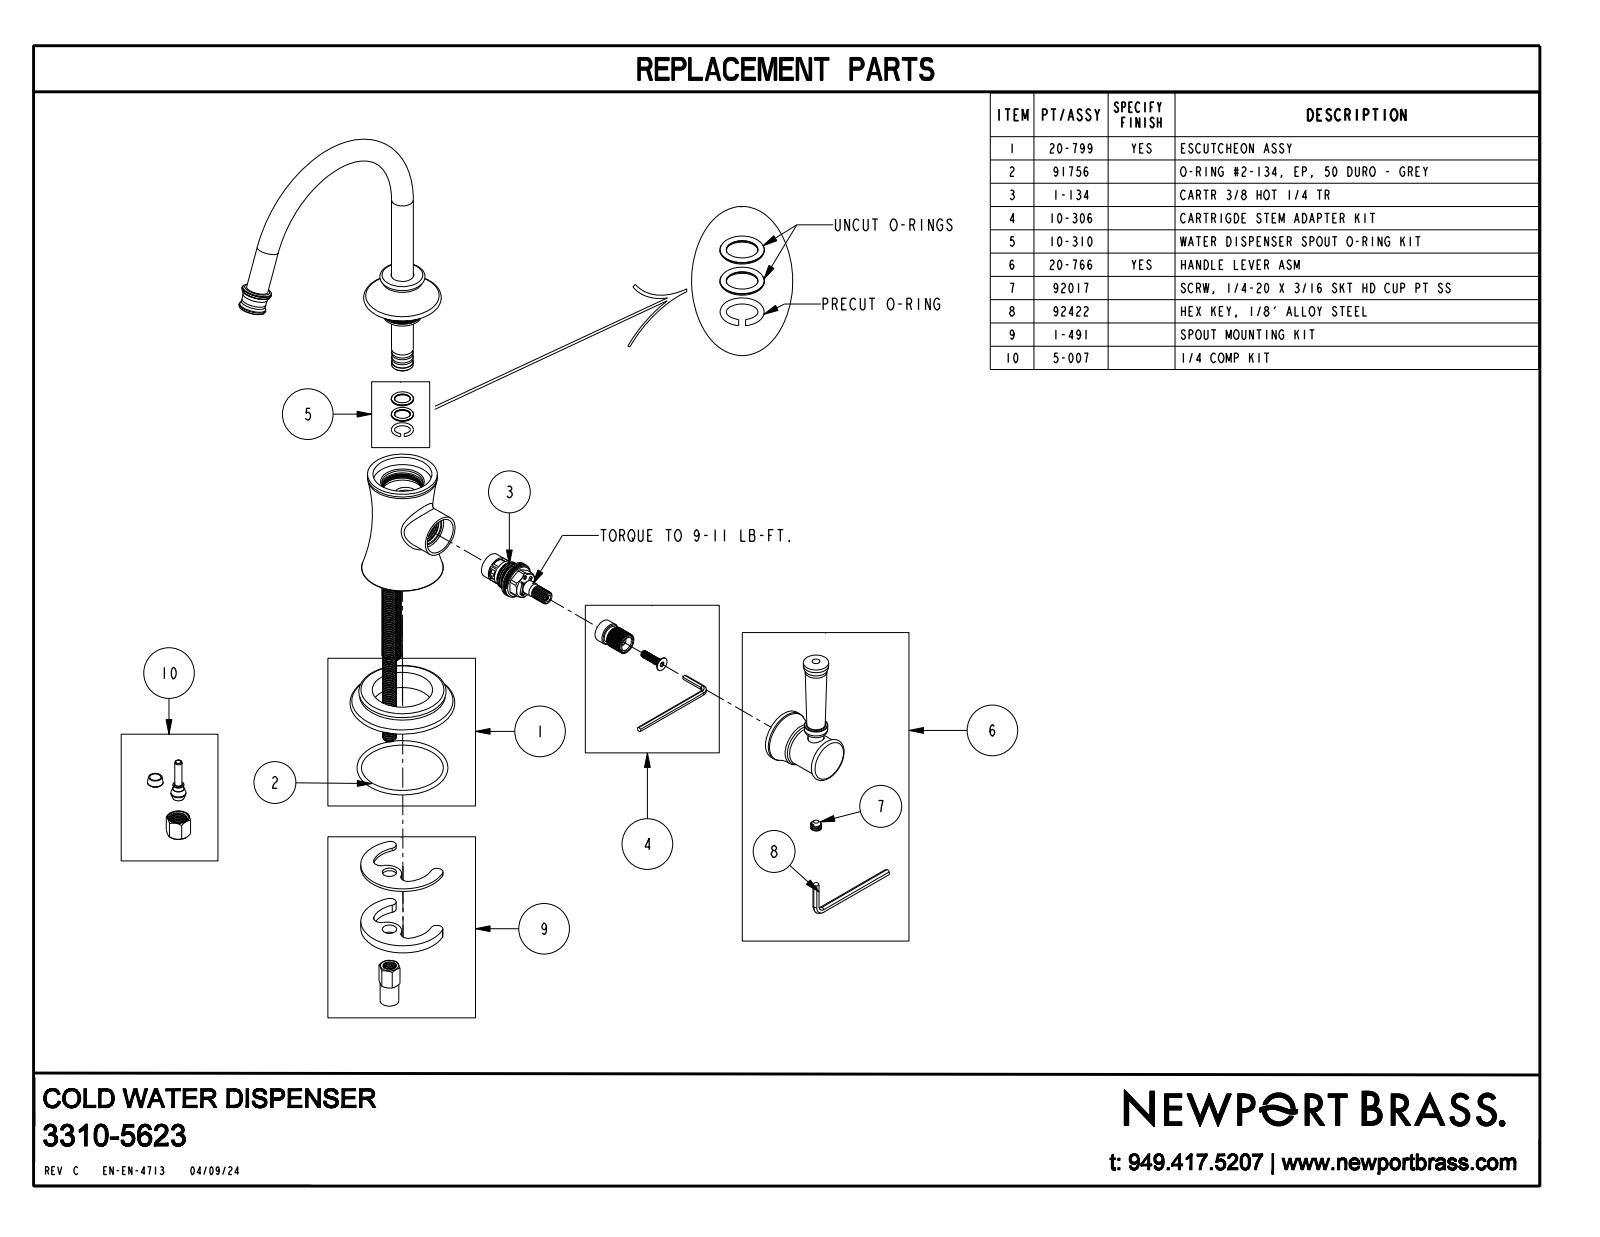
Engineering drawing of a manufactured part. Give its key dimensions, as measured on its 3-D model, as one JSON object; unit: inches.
{"part_name": "3310-5623", "step_written_by": "CREO PARAMETRIC BY PTC INC, 2018400 (CONFIG_CONTROL_DESIGN)", "units": "inches", "bodies": {"solids": 1, "faces": 121, "planar": 15, "cylindrical": 26, "other": 80}, "overall_size": [9.75, 6.232, 3.798], "volume_in3": 11.03, "surface_area_in2": 56.31, "round_holes": [[0.375, 1], [0.52, 1], [1.64, 1]], "round_bosses_or_shafts": [[0.5, 2], [1.6, 1], [1.19, 1], [1, 1], [0.96, 1], [0.9, 1], [0.58, 1], [0.536, 1]], "face_to_face_distances": [3.07, 0.02, 3.05, 3.725, 0.675, 0.655, 1.47, 0.425, 2.625, 2.645], "hole_center_spacings": [2.17]}
